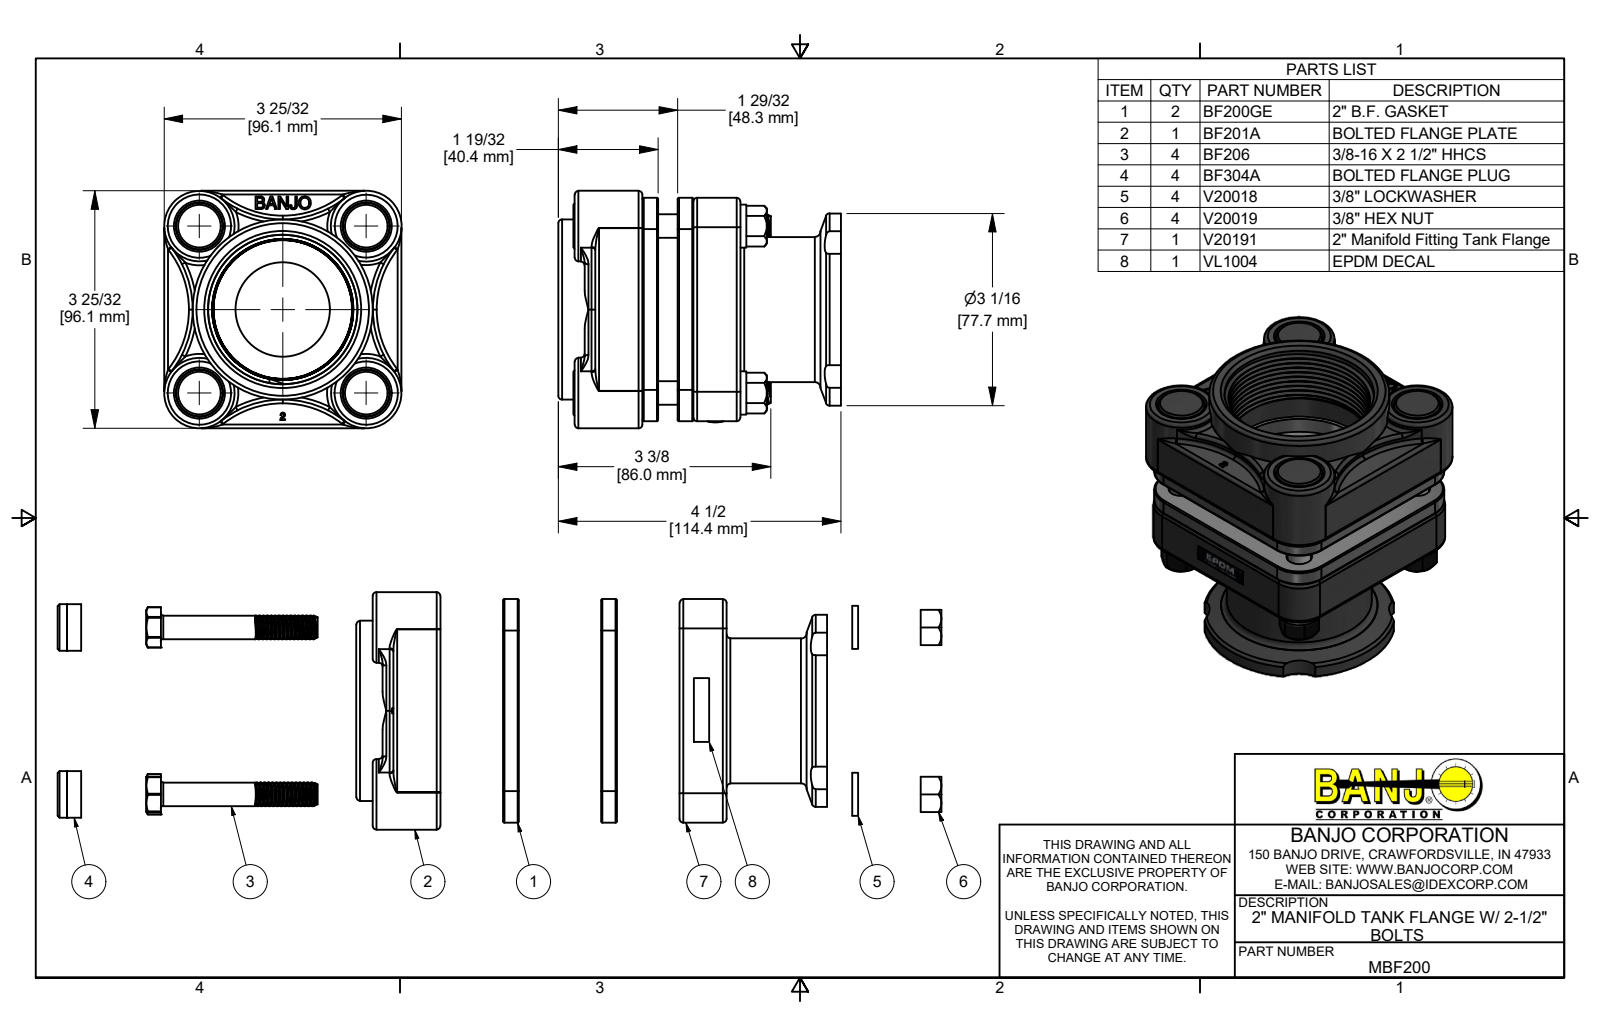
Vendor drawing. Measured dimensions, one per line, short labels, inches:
name: MBF200; BF201A; BF200GE; BF206 (+5 more)
written by: Autodesk Inventor 2019 (AUTOMOTIVE_DESIGN)
unit: in
bodies: 21 solids, 1125 faces (318 planar, 356 cylindrical, 451 other)
size: 4.503 × 3.784 × 3.784
volume: 27.34 in³; area: 198.2 in²
holes: 4× ⌀0.307, 4× ⌀0.38, 4× ⌀0.385, 4× ⌀0.406, 4× ⌀0.41, 4× ⌀0.715, 4× ⌀0.75, 1× ⌀1.5, 1× ⌀2.19, 1× ⌀2.25
bosses: 60× ⌀0.324, 4× ⌀1.125, 4× ⌀0.742, 4× ⌀0.687, 4× ⌀0.375, 1× ⌀2.87, 1× ⌀2.31
rounds: 24× R0.06, 16× R0.02, 8× R0.162, 4× R0.32, 4× R0.45, 4× R0.469, 4× R0.5, 4× R1.6
face distances: 0.563, 0.813, 0.25, 0.75, 1, 1.313, 1.563, 0.313, 0.111, 3.671
hole spacings: 1.88, 2.659, 3.761
